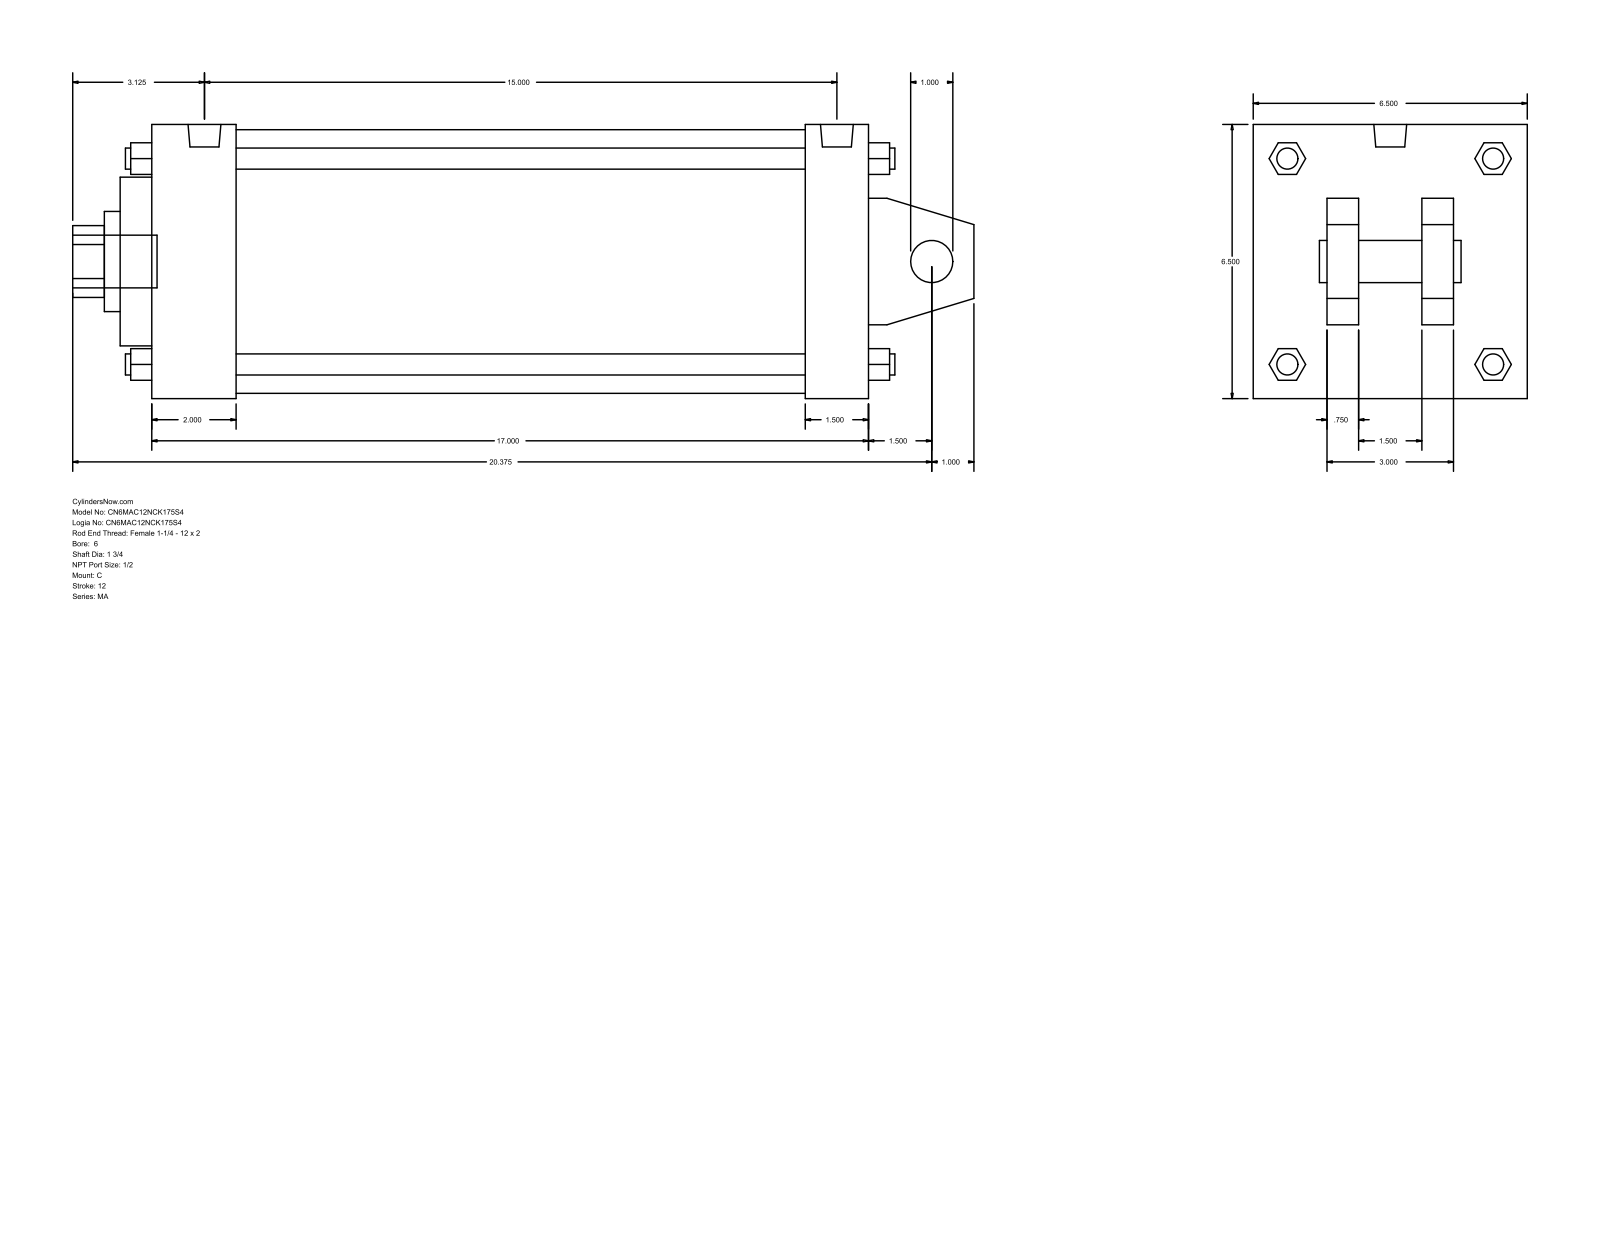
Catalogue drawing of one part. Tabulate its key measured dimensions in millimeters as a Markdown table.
| quantity | value |
| --- | --- |
| part name | MA_C__0600_1.75 |
| STEP written by | GSSL Pune (CONFIG_CONTROL_DESIGN) |
| units | millimeters |
| bodies | 0 solids, 141 faces (109 planar, 32 cylindrical, 0 other) |
| overall size | 542.92 × 165.1 × 165.1 |
| round holes (diameter × count) | 25.4 × 1, 44.45 × 1, 60.33 × 1, 101.6 × 1, 158.75 × 1 |
| round bosses / shafts (diameter × count) | 17.46 × 4, 12.7 × 4, 19.77 × 2, 31.75 × 1 |
| partial cylindrical surfaces (radius × count) | 21.63 × 1 |
| main face-to-face distances | 165.1, 431.81, 19.05, 101.6, 63.5, 50.8, 44.45, 120.65, 393.7, 57.15 |
